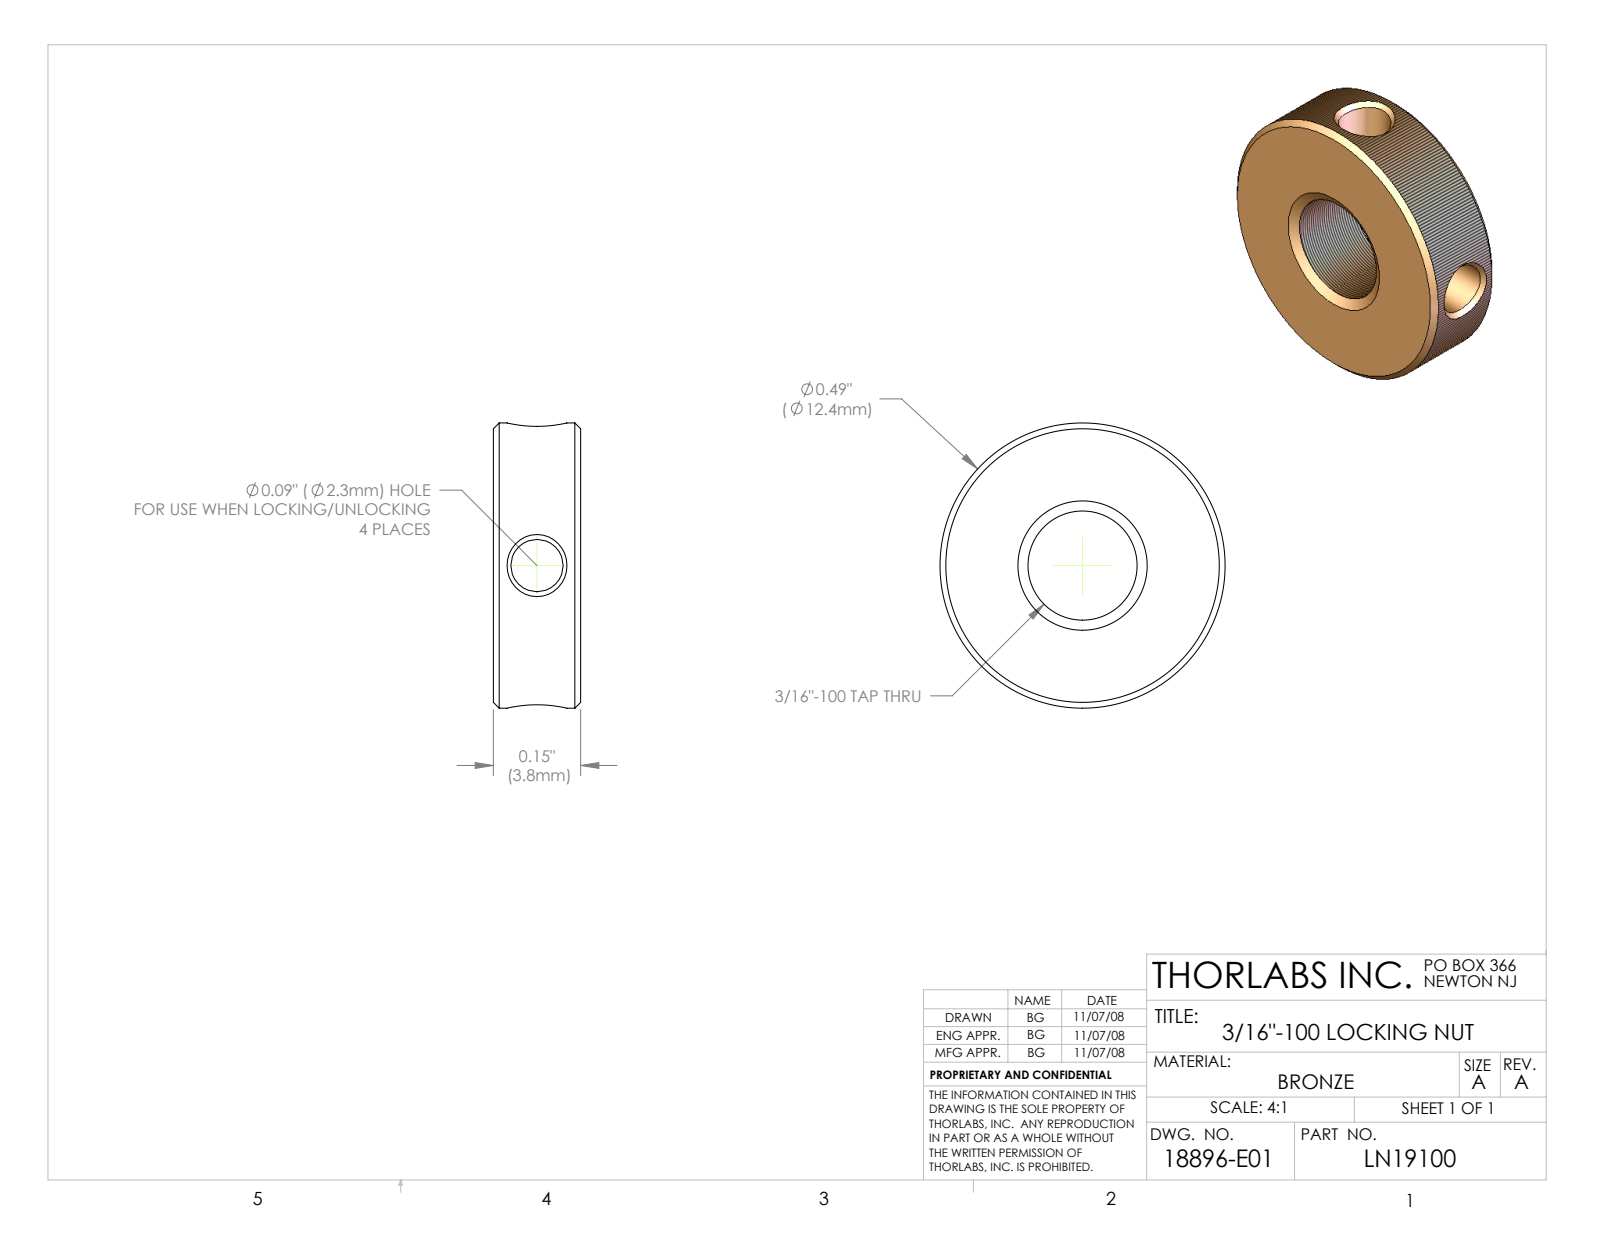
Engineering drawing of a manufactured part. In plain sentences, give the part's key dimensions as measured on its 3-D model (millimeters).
The part is named "18896-E0W". Its 3-D file was written by "SolidWorks 2007 (AUTOMOTIVE_DESIGN)". It is 1 solid with 34 faces: 6 planar, 12 cylindrical and 16 other. Overall it measures 12.45 by 12.45 by 3.81 millimeters. Its volume is 349 cubic millimeters and its surface area 464 square millimeters. Round holes: 2 of diameter 2.29, 1 of diameter 4.76. Round bosses or shafts: 1 of diameter 12.45. The main face-to-face distances are 3.8, 7.36.
